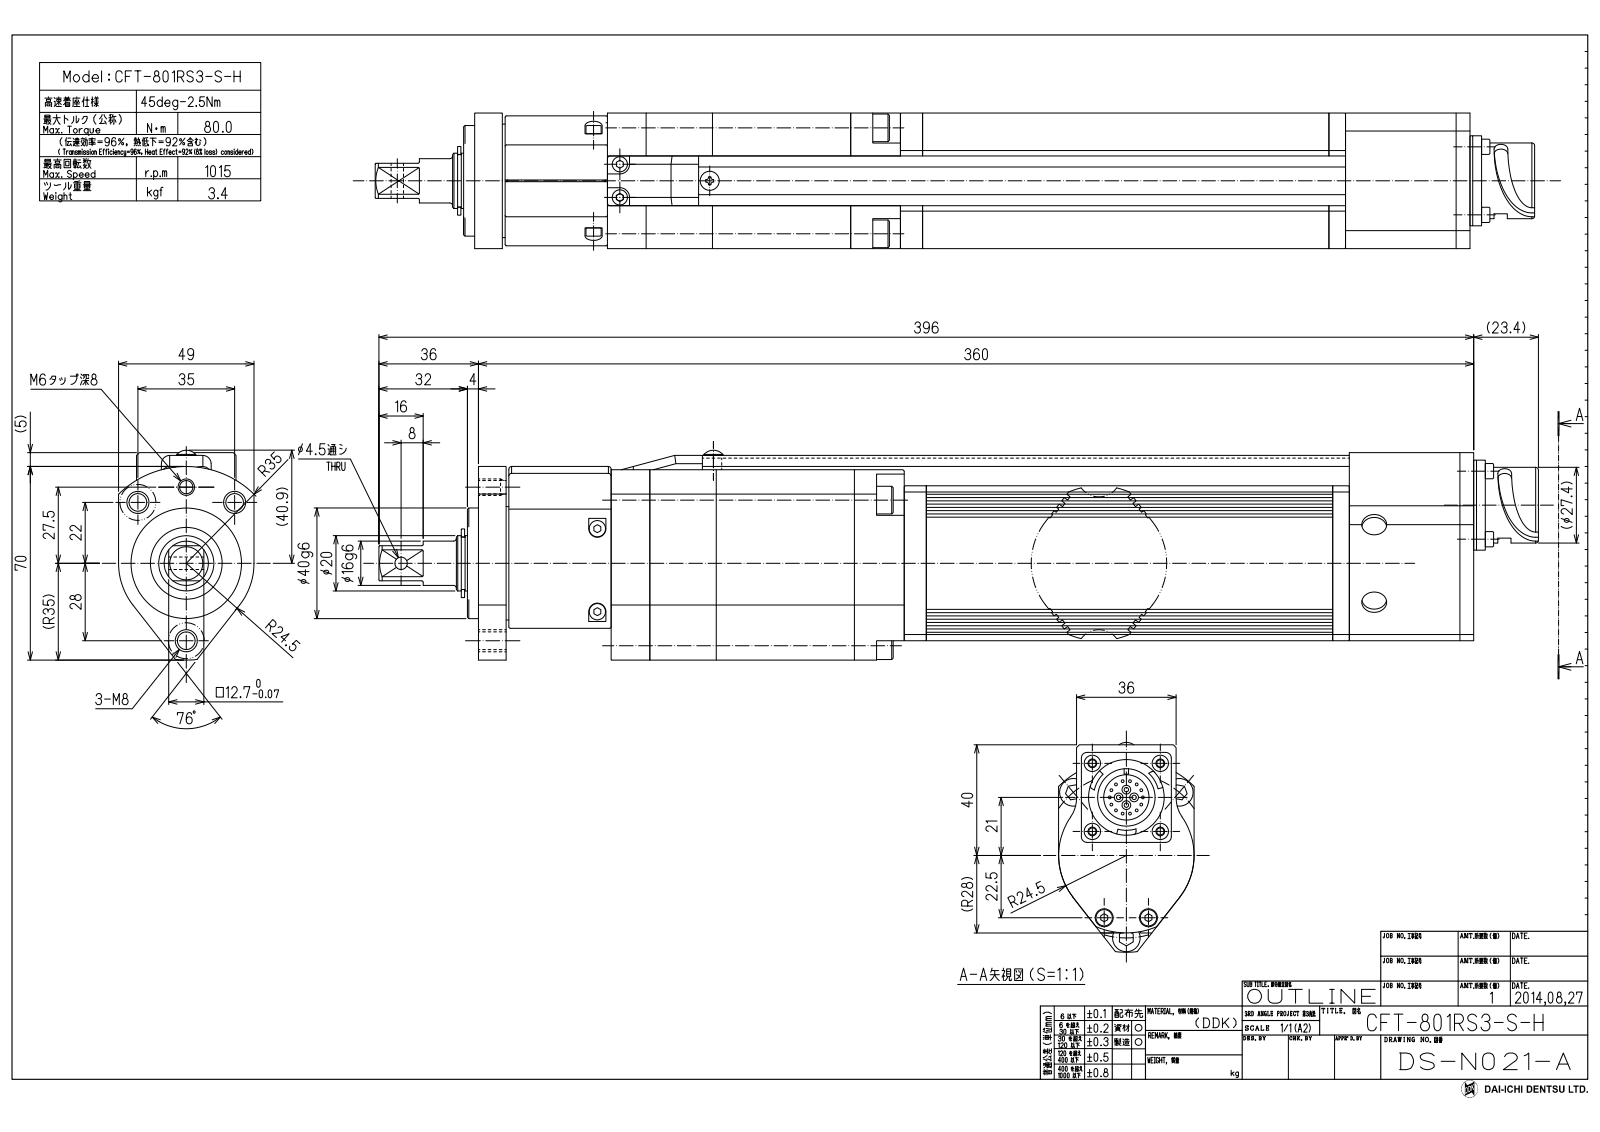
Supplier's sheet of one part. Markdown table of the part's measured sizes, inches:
| quantity | value |
| --- | --- |
| part name | CFT-801RS3-S-H(DS-N021-B+D)_OUTLINE_20201120 |
| STEP written by | Autodesk Inventor 2021 (AUTOMOTIVE_DESIGN) |
| units | inches |
| bodies | 1 solid, 667 faces (439 planar, 143 cylindrical, 85 other) |
| overall size | 16.512 × 2.986 × 1.929 |
| volume | 54.15 in³ |
| surface area | 153.6 in² |
| round holes (diameter × count) | 0.194 × 4, 0.354 × 4, 0.262 × 3, 0.051 × 2, 0.256 × 2, 0.177 × 1, 0.819 × 1, 0.827 × 1 |
| round bosses / shafts (diameter × count) | 0.039 × 14, 0.217 × 10, 0.315 × 4, 0.063 × 4, 0.394 × 3, 1.85 × 1, 1.614 × 1, 1.575 × 1 |
| partial cylindrical surfaces (radius × count) | 0.079 × 6, 0.098 × 4, 0.118 × 4, 0.039 × 3, 0.217 × 3, 0.122 × 2, 0.138 × 2, 0.157 × 2 |
| main face-to-face distances | 0.059, 0.039, 1.929, 0.61, 1.319, 1.93, 0.02, 0.472, 0.118, 0.866 |
| hole center spacings | 0.074, 0.382, 0.426, 0.69, 0.722, 0.759, 0.778, 0.94 |
